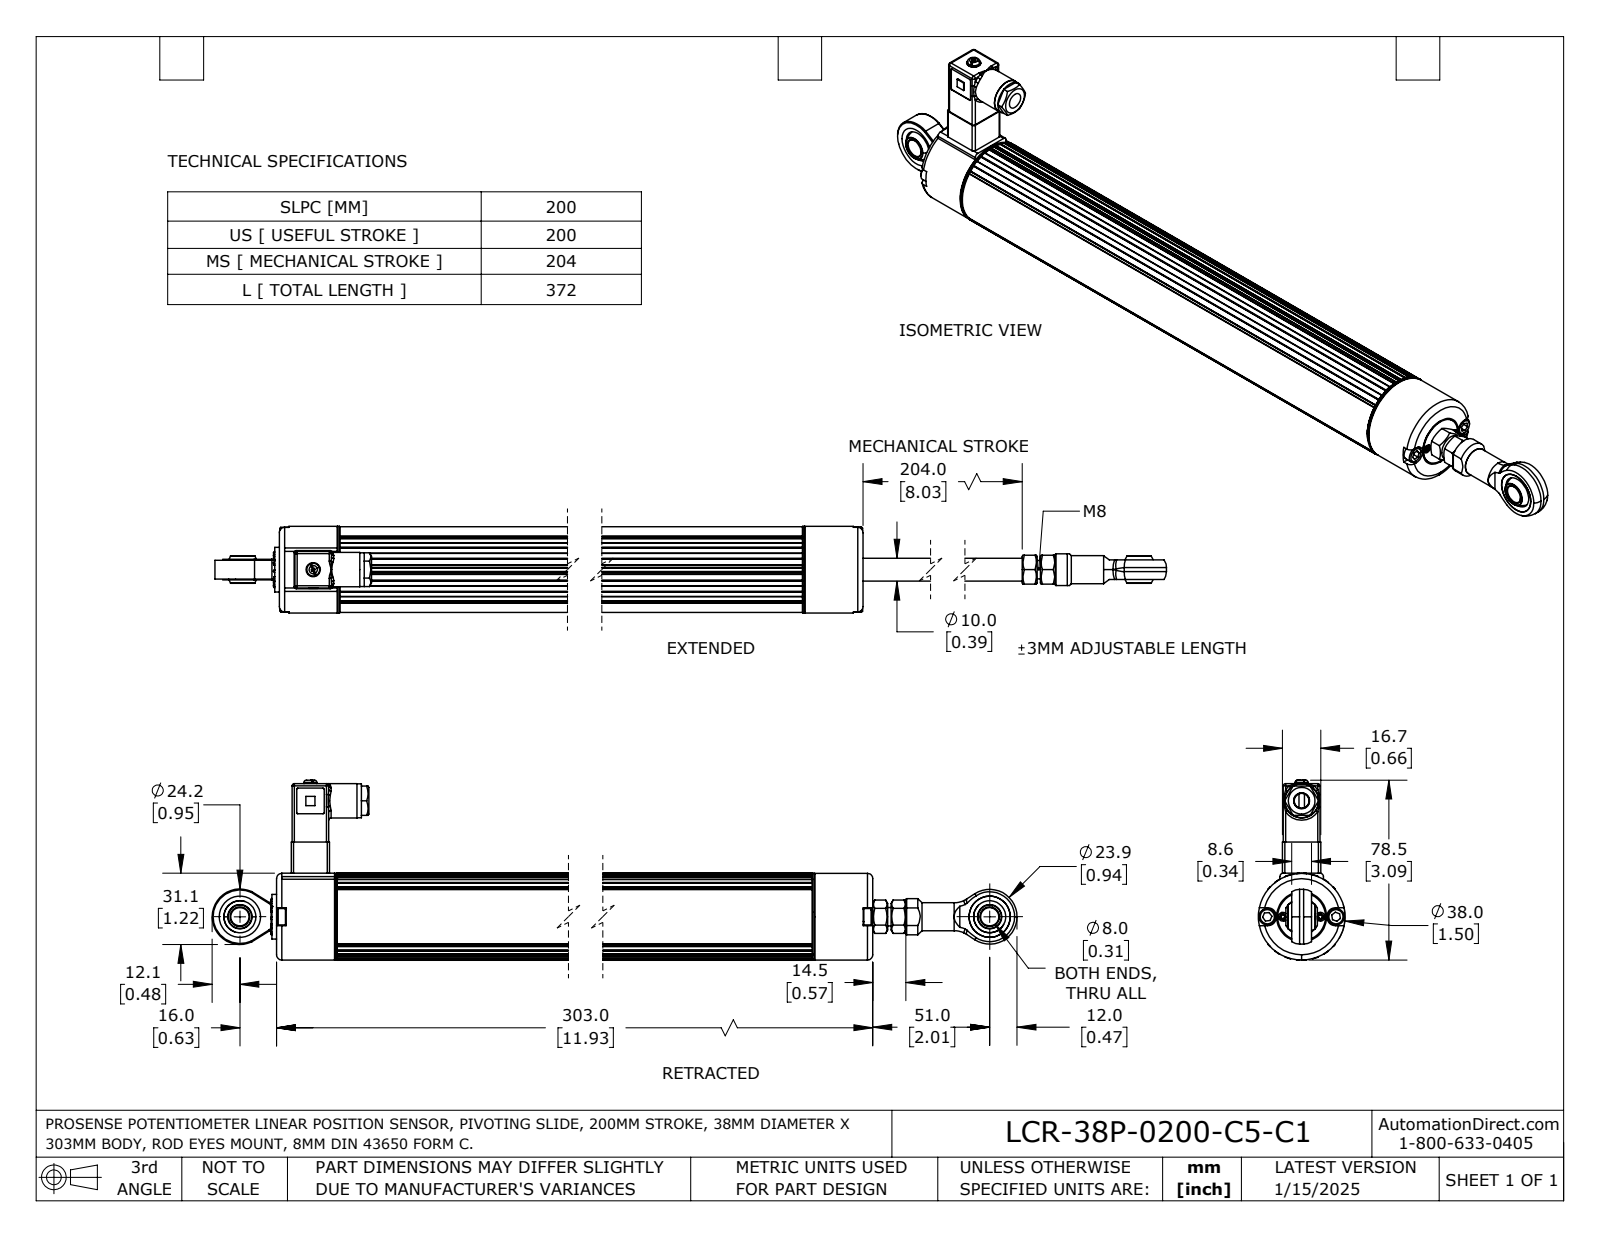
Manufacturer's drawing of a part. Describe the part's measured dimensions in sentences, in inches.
The part is named "LCR-38P-0200-C5-C1". Its 3-D file was written by "SolidWorks 2023 (AUTOMOTIVE_DESIGN)". It is 11 solids with 657 faces: 295 planar, 210 cylindrical and 152 other. Overall it measures 15.514 by 3.093 by 1.488 inches. Its volume is 21.64 cubic inches and its surface area 108.5 square inches. Round holes: 6 of diameter 0.102, 4 of diameter 0.091, 3 of diameter 0.315, 3 of diameter 0.551, 2 of diameter 0.094, 2 of diameter 0.1, 2 of diameter 0.111, 2 of diameter 0.134, 2 of diameter 0.152, 2 of diameter 0.165, 1 of diameter 0.079, 1 of diameter 0.118. Round bosses or shafts: 6 of diameter 0.063, 4 of diameter 0.283, 4 of diameter 0.15, 2 of diameter 0.48, 2 of diameter 0.079, 1 of diameter 1.488, 1 of diameter 0.823, 1 of diameter 0.768. Partial cylindrical surfaces (rounded edges, fillets, slot ends): 32 of radius 0.008, 20 of radius 0.039, 12 of radius 0.02, 6 of radius 0.016, 2 of radius 0.012, 2 of radius 0.059, 2 of radius 0.083, 2 of radius 0.098. The main face-to-face distances are 9.843, 1.043, 10.886, 0.031, 0.045, 0.612, 0.598, 0.014, 0.644, 0.138. The hole center spacings are 0.632, 0.075, 0.634, 0.264, 0.268, 0.285, 0.323, 0.394.
